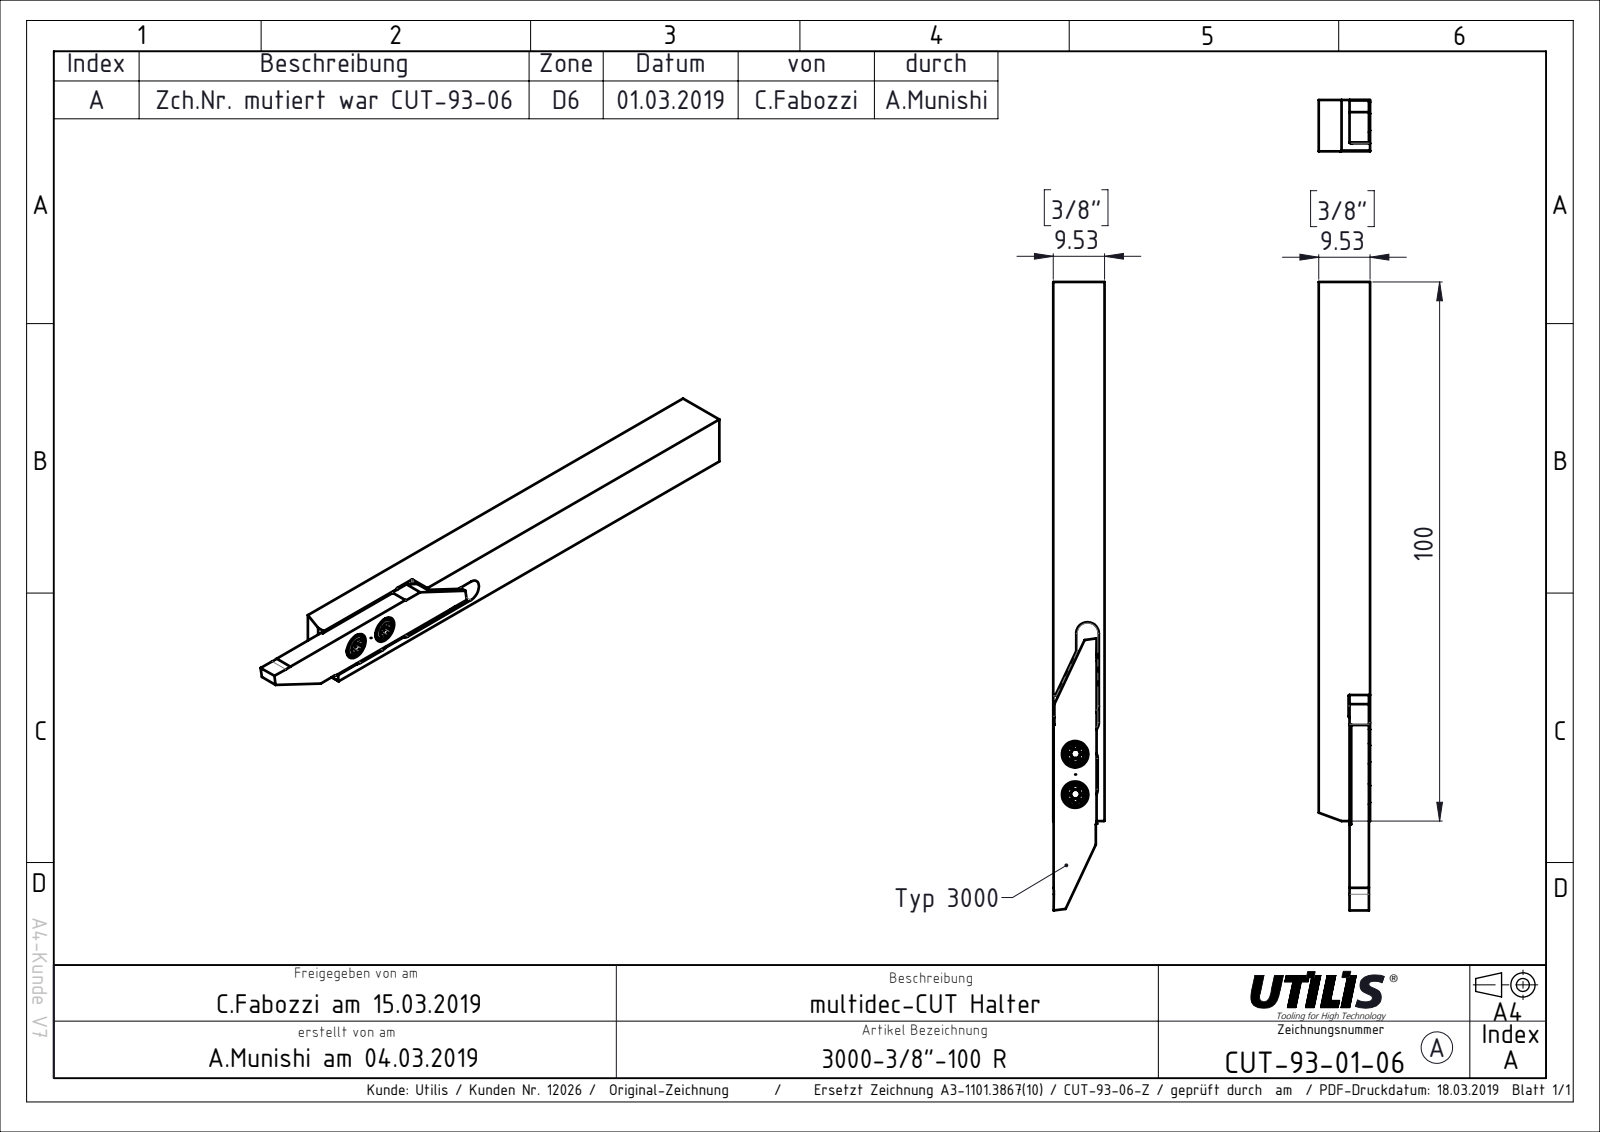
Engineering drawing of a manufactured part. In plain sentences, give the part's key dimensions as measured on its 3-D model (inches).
The part is named "CUT-Vorlage 3000 R+L Lang Kunde; CUT-93-Kunde; CUT-93-06; CUT-Vorlage 3000 R+L Lang Kunde_R-Lang (+1 more)". Its 3-D file was written by "SolidWorks 2015 (CONFIG_CONTROL_DESIGN)". It is 2 solids with 55 faces: 36 planar, 19 cylindrical and 0 other. Overall it measures 4.587 by 0.375 by 0.375 inches. Its volume is 0.552 cubic inches and its surface area 8.065 square inches. Round holes: 2 of diameter 0.098, 2 of diameter 0.193. Partial cylindrical surfaces (rounded edges, fillets, slot ends): 4 of radius 0.083, 2 of radius 0.006, 2 of radius 0.394. The main face-to-face distances are 0.375, 0.15, 0.226, 0.142, 0.367, 0.06, 0.315, 0.043, 0.018, 0.333. The hole center spacings are 0.148, 0.295.
